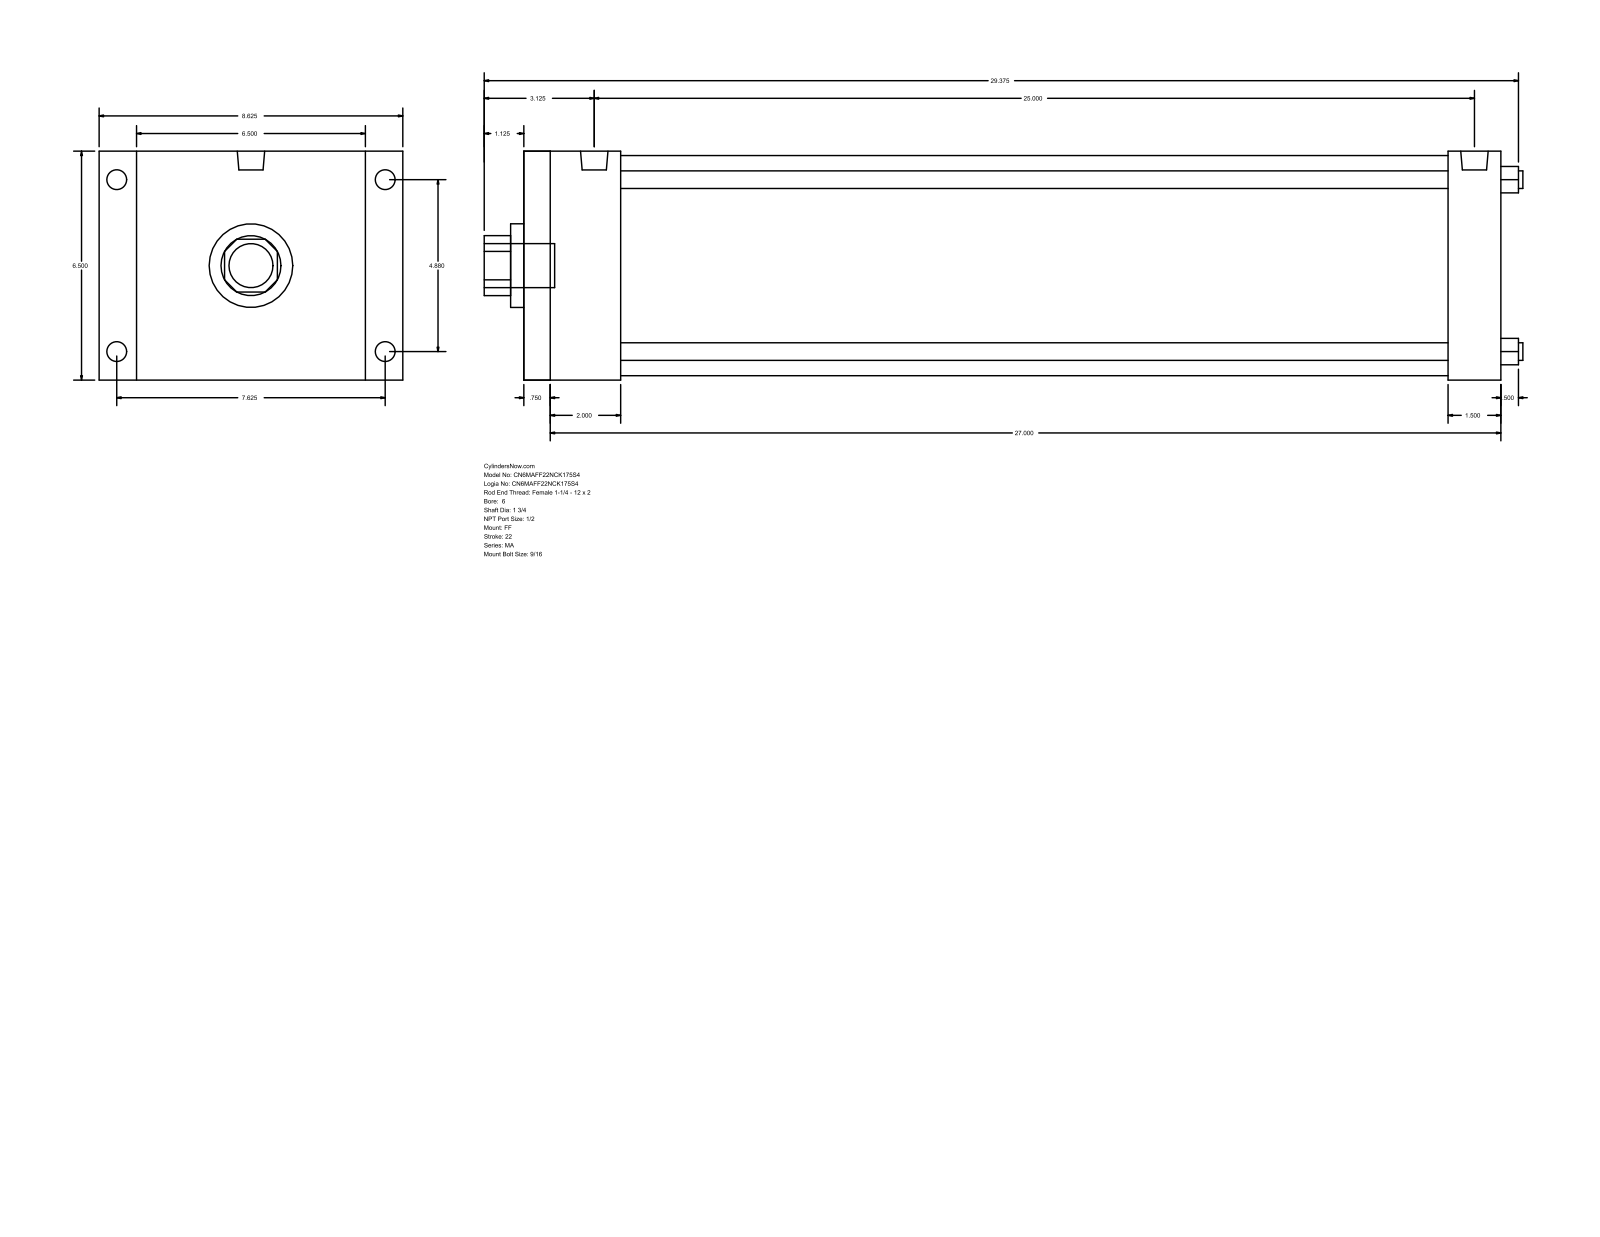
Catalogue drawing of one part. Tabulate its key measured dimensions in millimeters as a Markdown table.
| quantity | value |
| --- | --- |
| part name | MA_FF__0600_1.75 |
| STEP written by | GSSL Pune (CONFIG_CONTROL_DESIGN) |
| units | millimeters |
| bodies | 0 solids, 92 faces (64 planar, 28 cylindrical, 0 other) |
| overall size | 749.3 × 219.07 × 165.1 |
| round holes (diameter × count) | 12.7 × 4, 44.45 × 1, 60.33 × 1, 158.75 × 1 |
| round bosses / shafts (diameter × count) | 17.46 × 4, 14.29 × 4, 19.77 × 2, 31.75 × 1 |
| partial cylindrical surfaces (radius × count) | 21.63 × 1 |
| main face-to-face distances | 165.1, 704.85, 19.05, 685.8, 50.8, 69.85, 635, 666.76, 647.71, 596.91 |
| hole center spacings | 87.65, 123.96, 175.31 |
